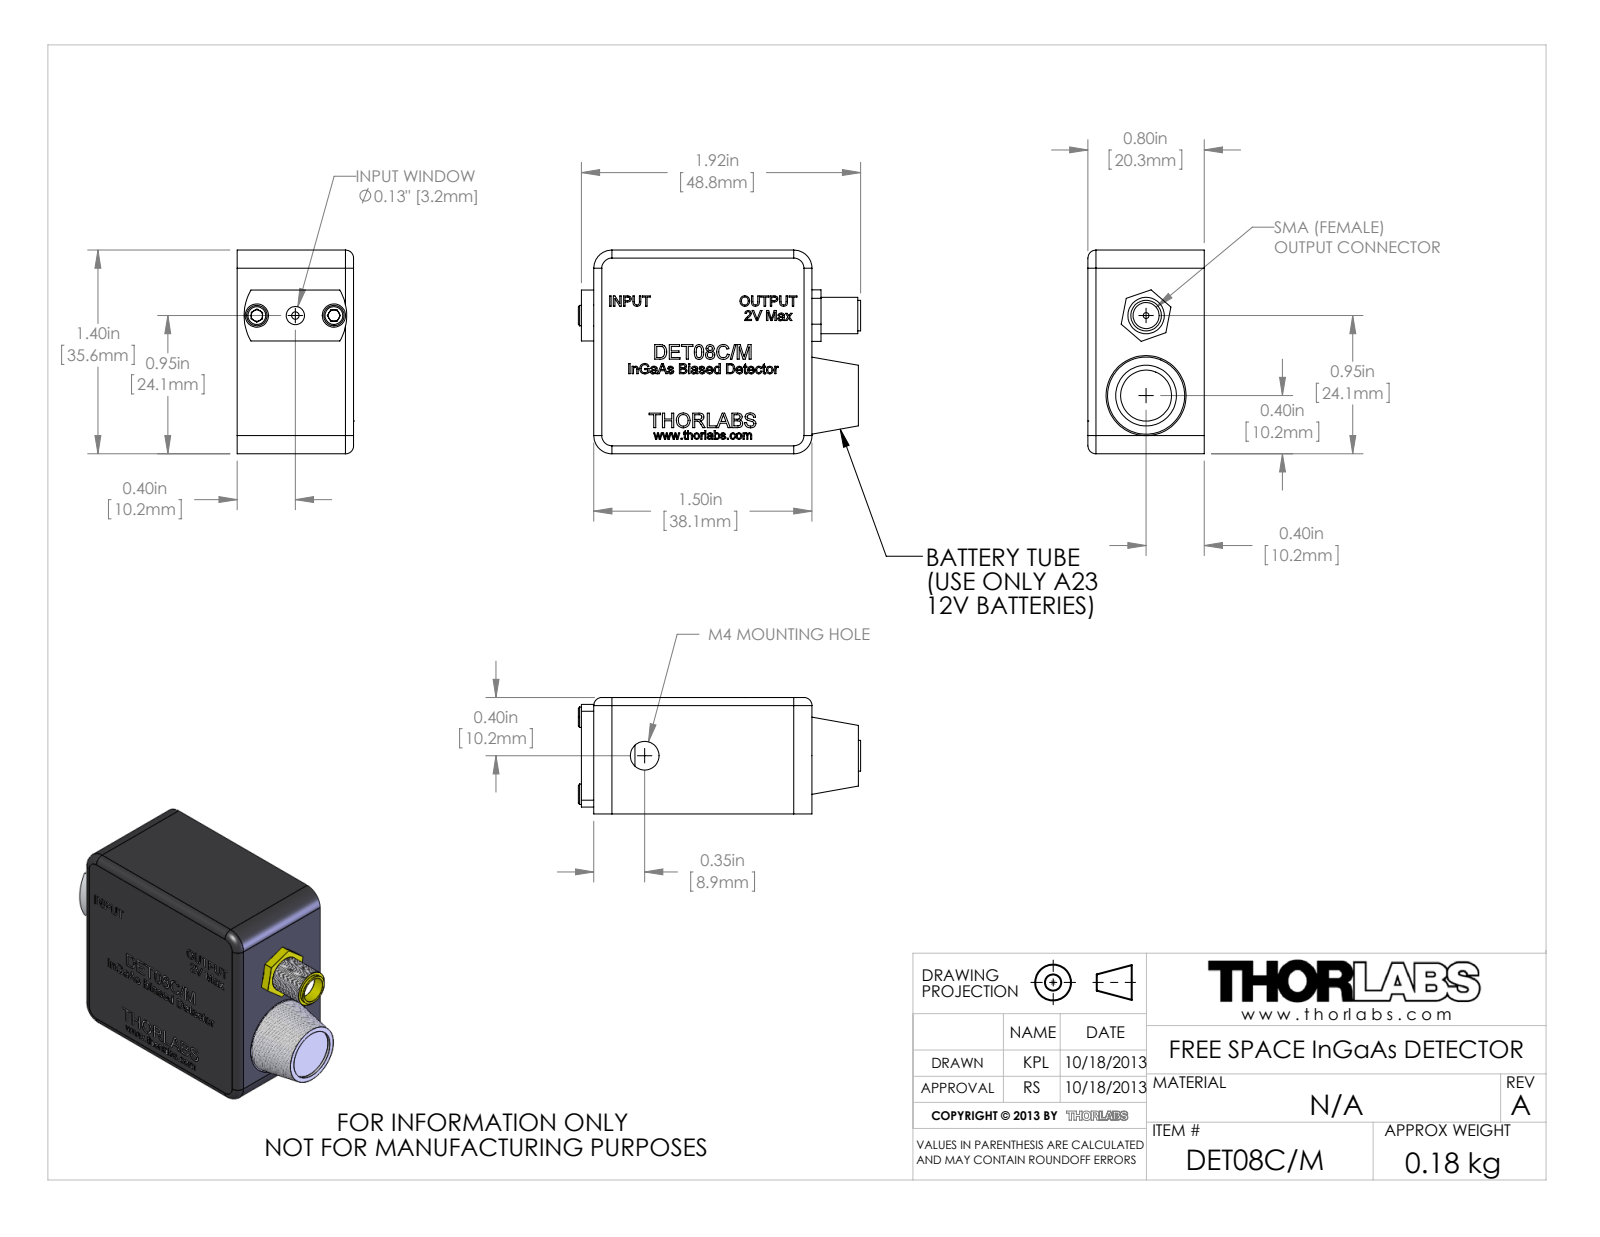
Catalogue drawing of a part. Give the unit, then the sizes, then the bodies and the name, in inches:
Units: inches
Overall size (bounding box): 1.941 × 1.4 × 0.8
Round holes (diameter × count): ⌀0.07 ×6, ⌀0.096 ×4, ⌀0.125 ×4, ⌀0.14 ×4, ⌀0.085 ×2, ⌀0.16 ×2, ⌀0.017 ×1, ⌀0.04 ×1, ⌀0.05 ×1, ⌀0.125 ×1, ⌀0.179 ×1, ⌀0.186 ×1
Round bosses / shafts (diameter × count): ⌀0.086 ×6, ⌀0.147 ×4, ⌀0.14 ×2, ⌀0.472 ×1, ⌀0.432 ×1, ⌀0.327 ×1, ⌀0.31 ×1, ⌀0.228 ×1
Partial cylindrical surfaces — rounded edges, fillets, slot ends (radius × count): R0.125 ×12, R0.032 ×4, R0.055 ×4, R0.08 ×4, R0.095 ×4, R0.06 ×2, R0.1 ×2, R0.008 ×1
Main face-to-face distances: 0.063, 0.737, 0.8, 1.4, 0.5, 0.563, 0.237, 0.1, 1.5, 1.3
Hole centre spacings: 1.698, 1.15, 1.25, 1.25, 0.265, 0.611, 1.15, 1.331
Volume: 1.051 in³ · Surface area: 20.94 in²
Bodies: 11 solids, 1673 faces (986 planar, 165 cylindrical, 522 other)
Part name (STEP PRODUCT): TTN020135; flat head screw_ai_CR-FHMS 0.086-56x0.188x0.188-N; socket head cap screw_ai_HX-SHCS 0.086-56x0.188x0.188-N; TTN020132 (+4 more)
STEP written by: SolidWorks 2012 (AUTOMOTIVE_DESIGN)
